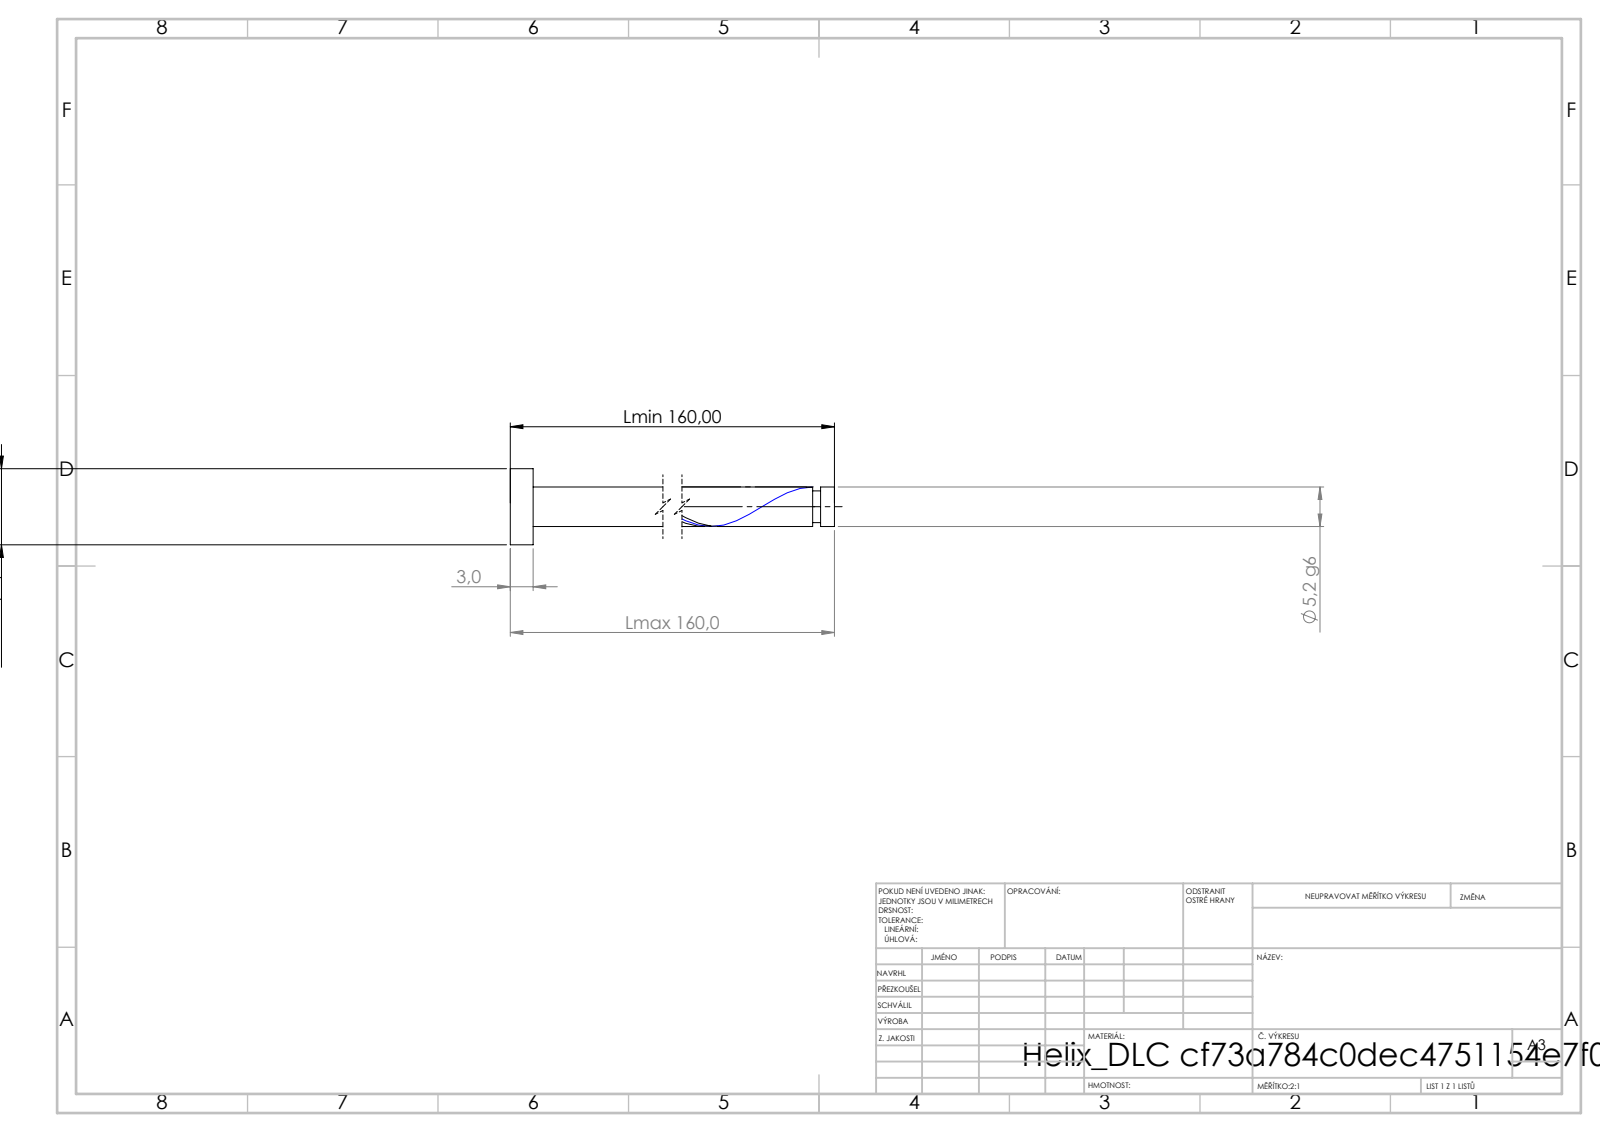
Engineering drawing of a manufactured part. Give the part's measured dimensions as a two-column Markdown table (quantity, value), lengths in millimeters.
| quantity | value |
| --- | --- |
| STEP written by | SolidWorks 2019 (CONFIG_CONTROL_DESIGN) |
| units | millimeters |
| bodies | 1 solid, 21 faces (6 planar, 14 cylindrical, 1 other) |
| overall size | 160 × 10 × 10 |
| volume | 3 529 mm³ |
| surface area | 2 877 mm² |
| round bosses / shafts (diameter × count) | 10 × 1, 5.2 × 1, 4.16 × 1 |
| main face-to-face distances | 3, 160, 157, 158.18, 155.18, 1.82, 157.14, 154.14, 1.04, 2.86 |
